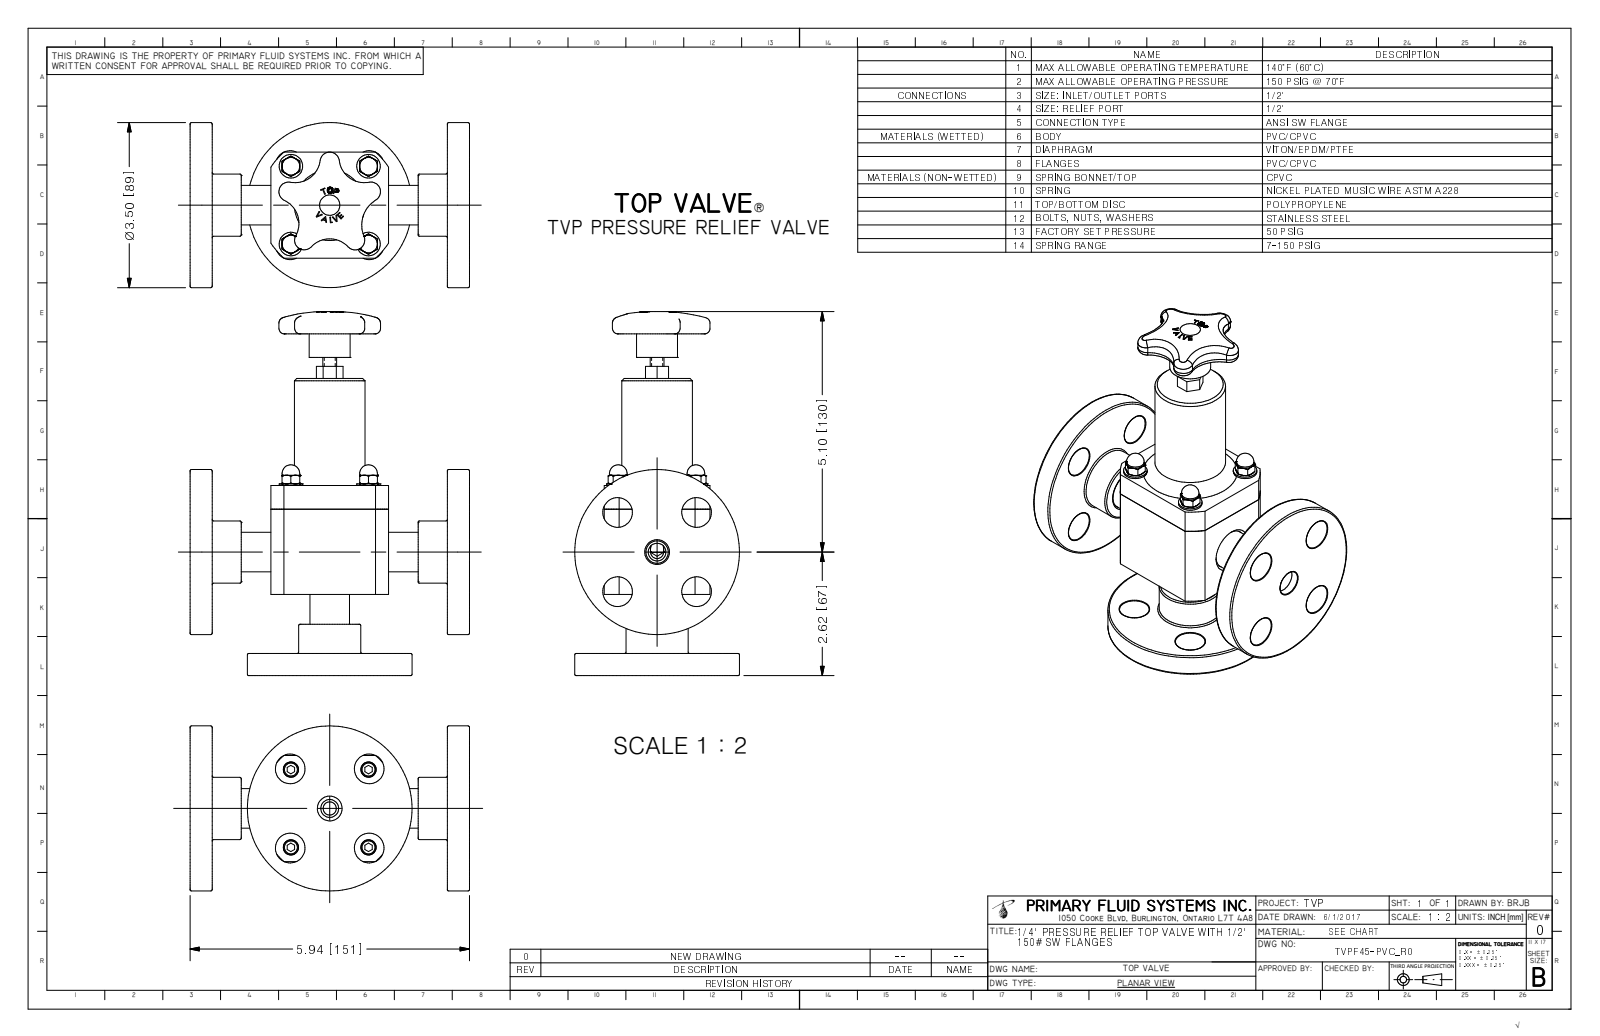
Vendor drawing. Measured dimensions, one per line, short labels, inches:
name: TVPF45-PVC_R0
written by: Autodesk Inventor 2009 (AUTOMOTIVE_DESIGN)
unit: in
bodies: 1 solid, 440 faces (160 planar, 66 cylindrical, 214 other)
size: 7.72 × 5.94 × 3.5
volume: 31.9 in³; area: 166.2 in²
holes: 8× ⌀0.63, 4× ⌀0.147, 2× ⌀0.526, 1× ⌀1.525
bosses: 4× ⌀0.5, 4× ⌀0.375, 4× ⌀0.312, 2× ⌀3.5, 2× ⌀1.32, 1× ⌀1.5, 1× ⌀0.87, 1× ⌀0.293
rounds: 5× R0.085, 5× R0.205, 4× R0.536, 4× R0.656, 1× R0.625, 1× R0.745, 1× R1.488
face distances: 0.47, 5.47, 1.72, 1.25, 5.94, 5, 4.22, 3.75, 2.25, 2.5
hole spacings: 1.188, 1.68, 1.665, 2.375, 0.02, 0.021, 1.167, 1.167
